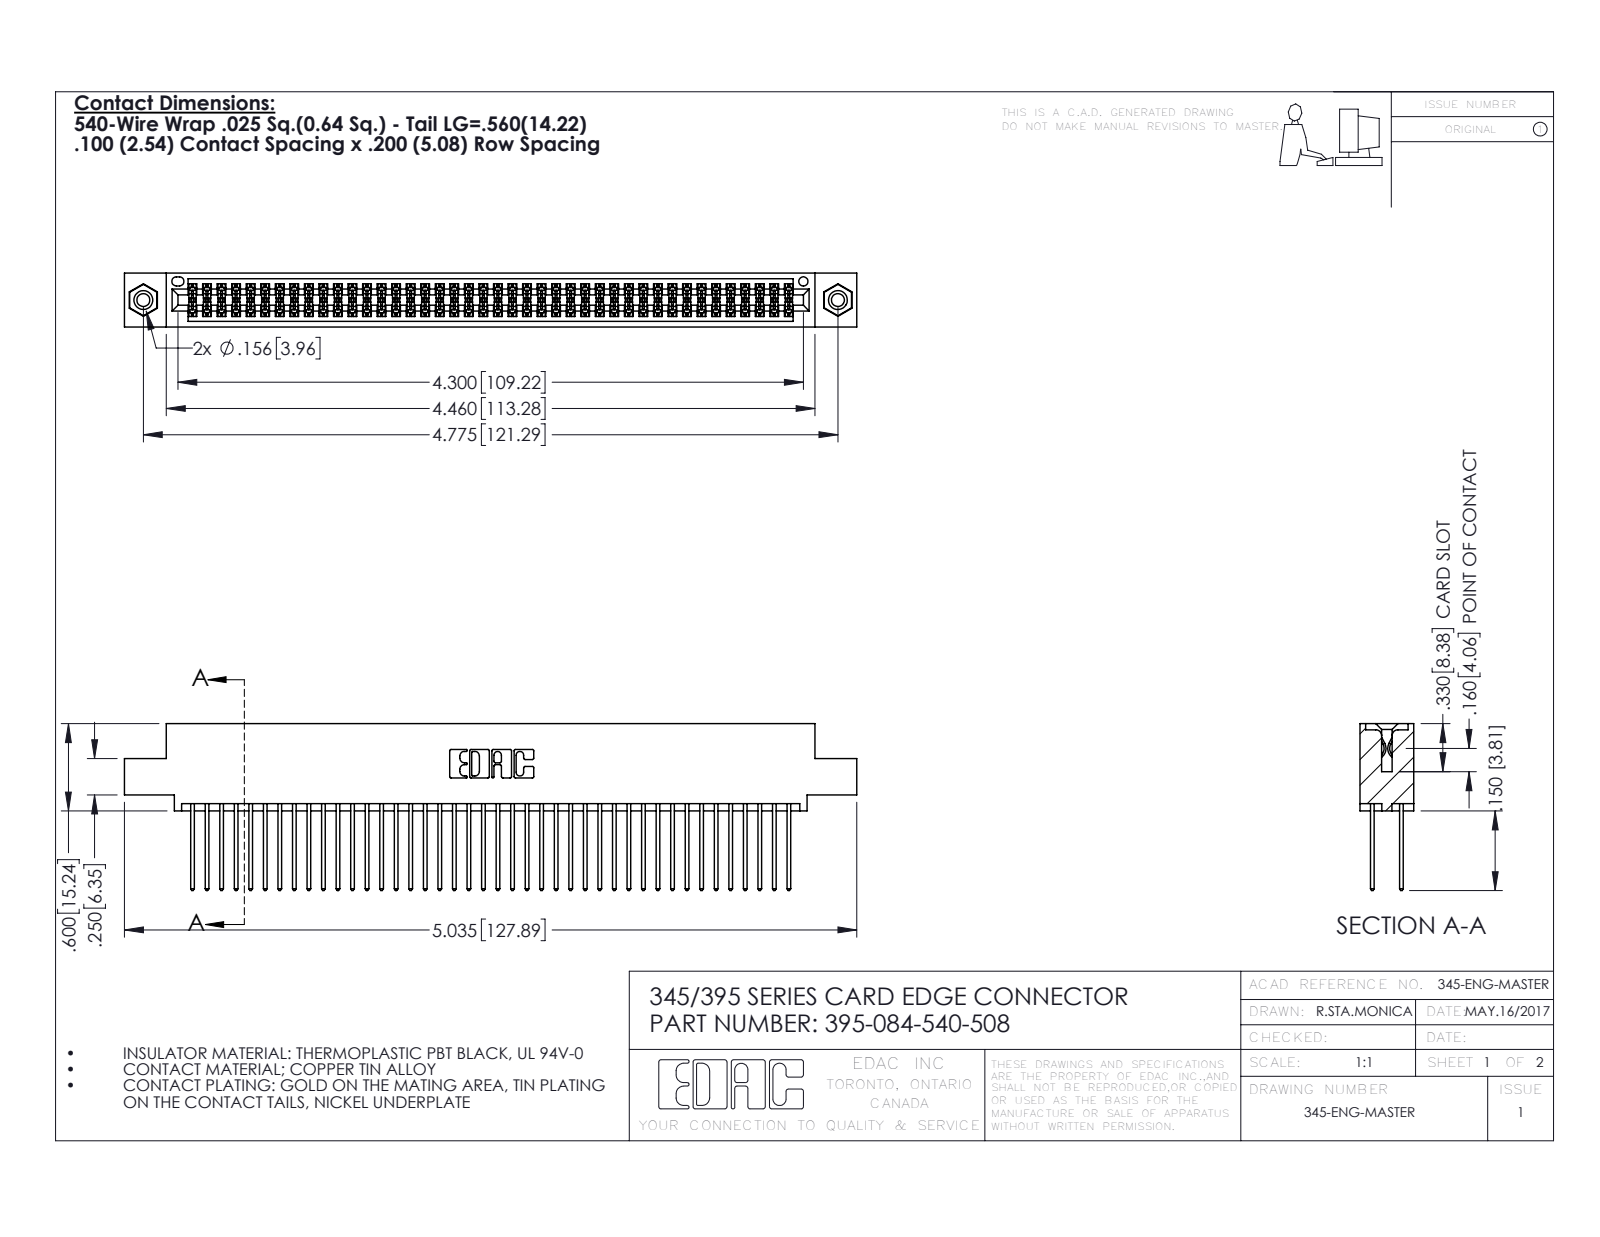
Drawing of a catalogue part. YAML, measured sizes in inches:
part_name: "345-250-001_345-250-003-102; 345-292-001_345-293-140; 345 Part_0.110 Offset - 0.156 Dia-TI; 395-084-540-508"
step_written_by: "SolidWorks 2016 (CONFIG_CONTROL_DESIGN)"
units: inches
bodies: {solids: 87, faces: 4390, planar: 2888, cylindrical: 1486, other: 16}
overall_size: [5.035, 1.147, 0.37]
volume: 0.773
surface_area: 31.46
round_holes:
  - {diameter: 0.089, count: 2}
  - {diameter: 0.125, count: 2}
  - {diameter: 0.156, count: 2}
  - {diameter: 0.064, count: 1}
round_bosses_or_shafts:
  - {diameter: 0.155, count: 2}
partial_cylinders:
  - {radius: 0.006, count: 126}
  - {radius: 0.01, count: 84}
  - {radius: 0.01, count: 22}
  - {radius: 0.007, count: 6}
  - {radius: 0.031, count: 6}
  - {radius: 0.026, count: 3}
  - {radius: 0.014, count: 2}
  - {radius: 0.019, count: 2}
face_to_face_distances: [0.072, 0.298, 0.2, 0.098, 0.272, 0.025, 0.37, 0.225, 0.175, 0.149]
hole_center_spacings: [0.27, 4.539, 4.775]
